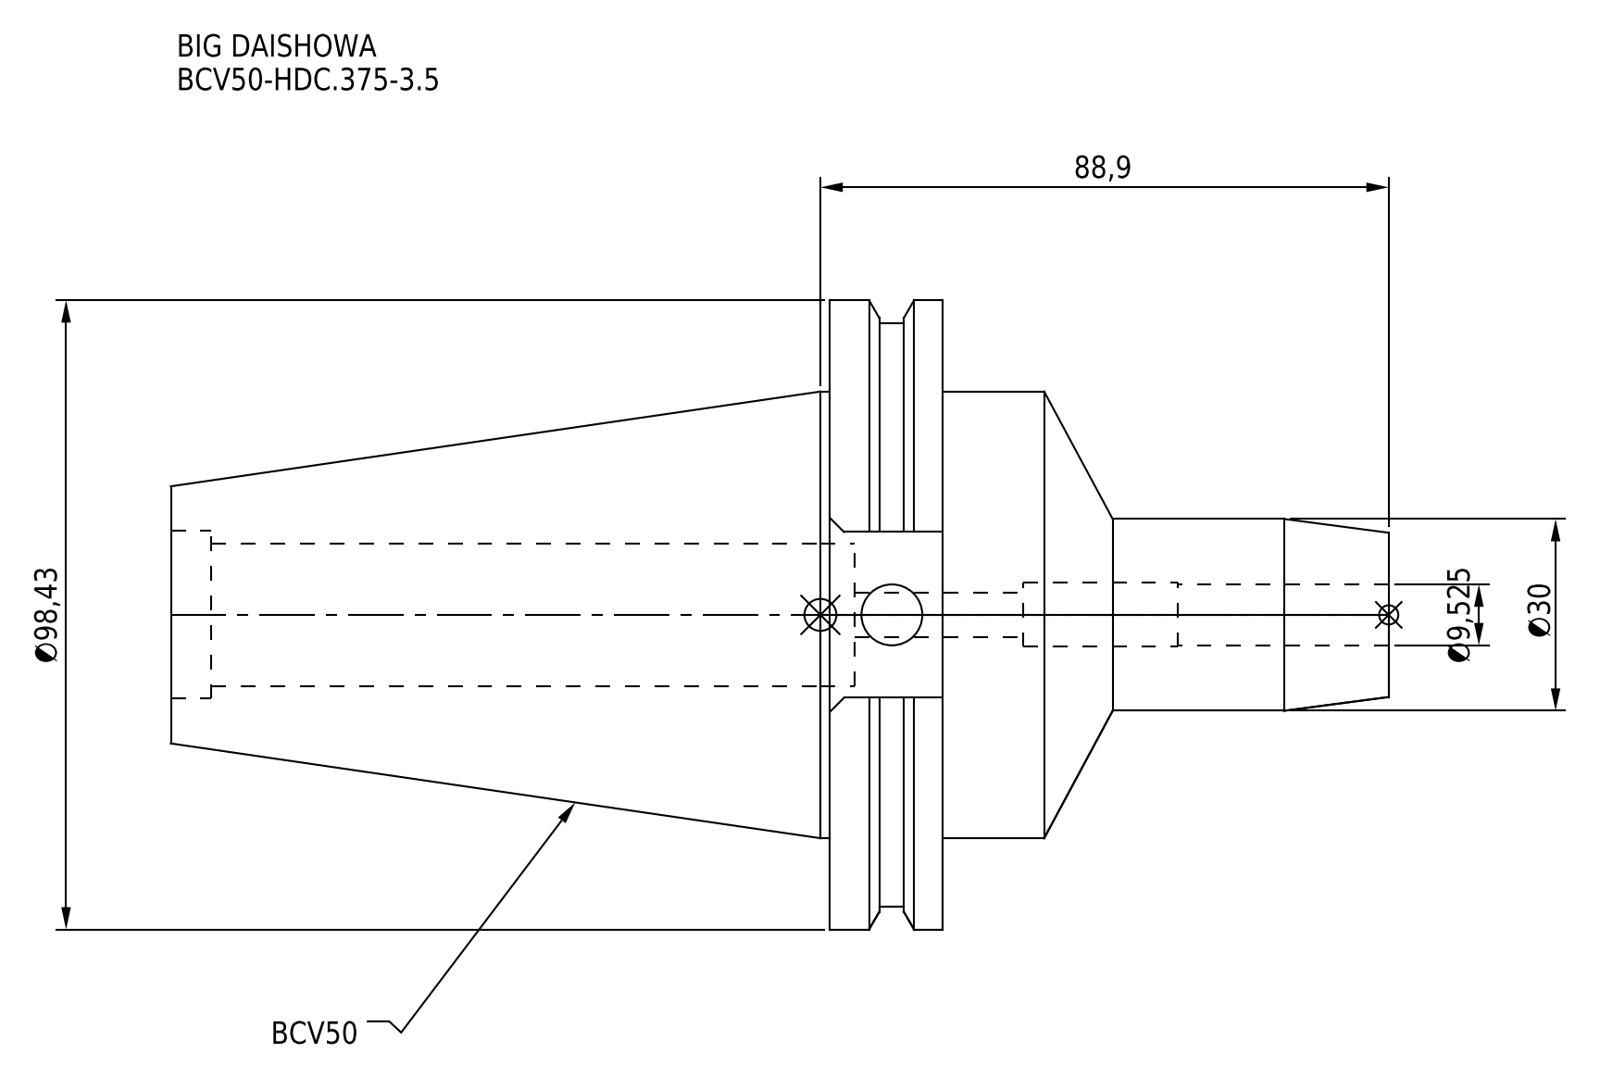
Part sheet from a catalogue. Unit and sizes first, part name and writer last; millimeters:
Units: millimetres
Overall size (bounding box): 190.5 × 98.42 × 94.95
Round holes (diameter × count): ⌀9.53 ×2, ⌀7 ×1, ⌀10 ×1, ⌀22.3 ×1, ⌀26.23 ×1
Round bosses / shafts (diameter × count): ⌀98.42 ×1, ⌀91.29 ×1, ⌀69.85 ×1, ⌀30 ×1
Main face-to-face distances: 17.55, 120.65, 103.1, 69.85, 87.4, 190.5, 72.95, 83.5, 13.65, 3.9
Volume: 435 261 mm³ · Surface area: 54 140 mm²
Bodies: 1 solid, 59 faces (23 planar, 26 cylindrical, 10 other)
Part name (STEP PRODUCT): BCV50-HDC_375-3_5
STEP written by: CREO PARAMETRIC BY PTC INC, 2016380 (AUTOMOTIVE_DESIGN)
